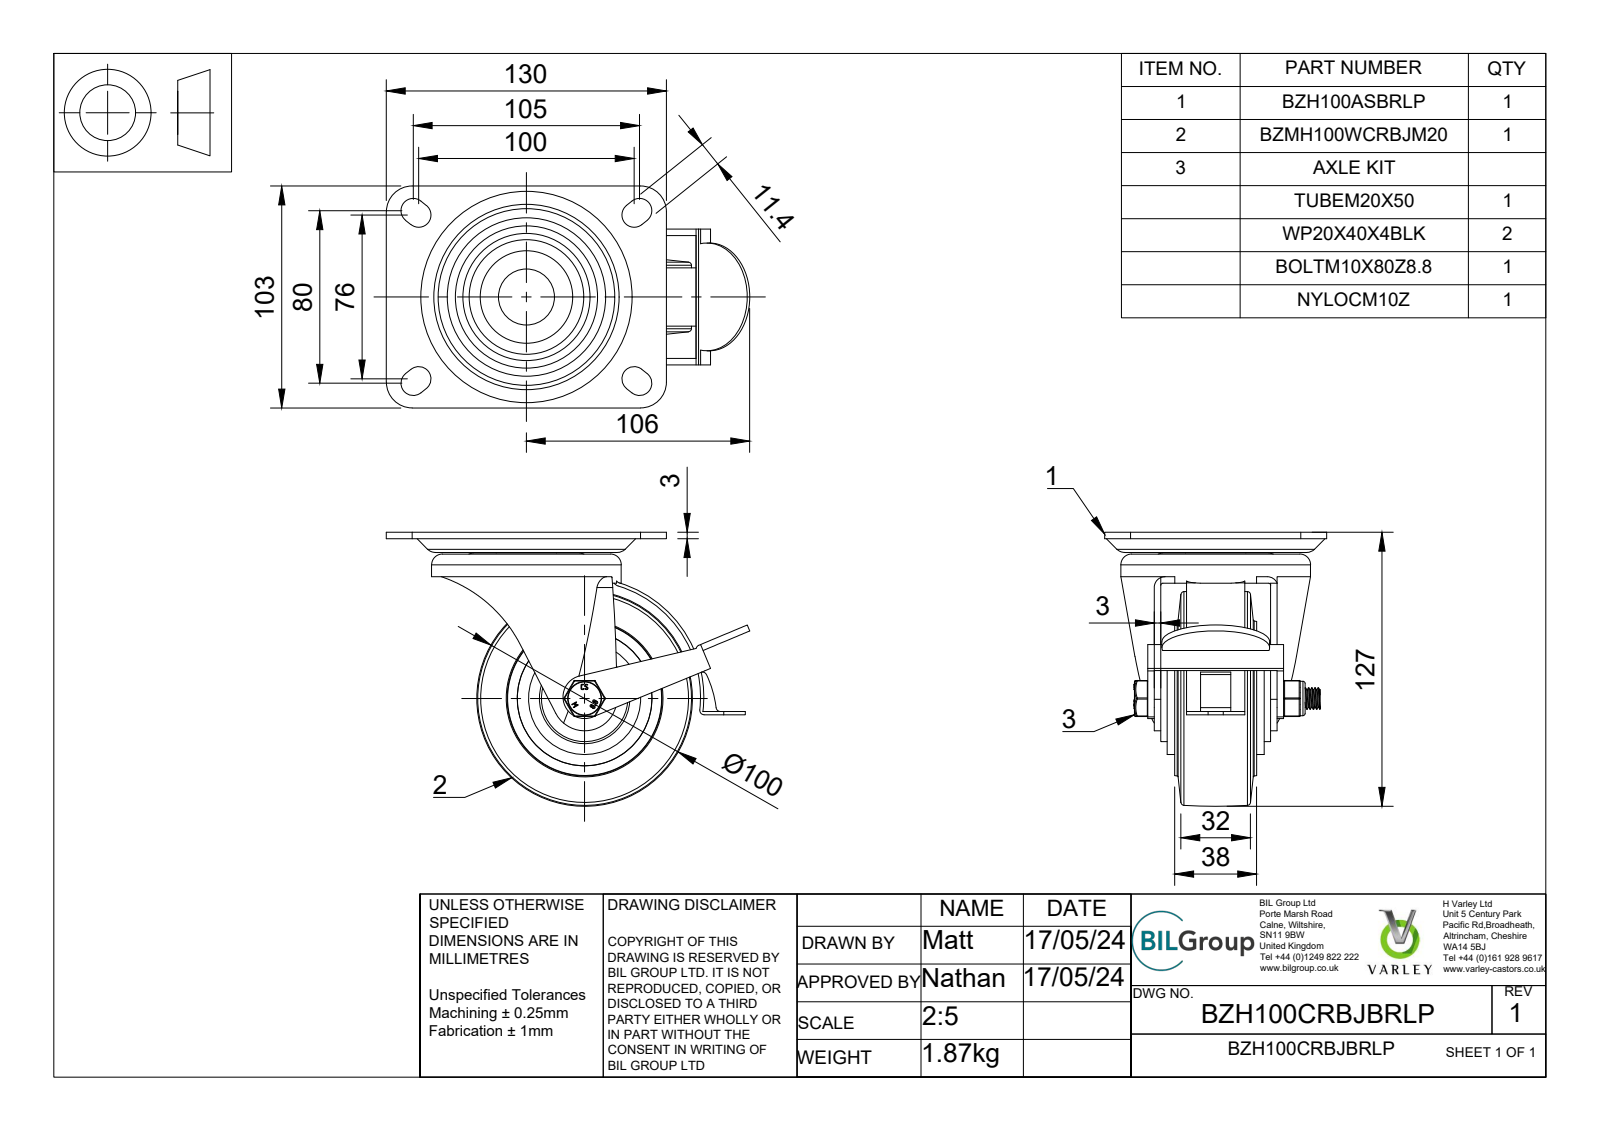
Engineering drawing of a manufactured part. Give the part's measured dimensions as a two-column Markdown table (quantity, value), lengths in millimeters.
| quantity | value |
| --- | --- |
| part name | BZH100CRBJBRLP v3; BZH100ASBRLP v1; ZINC PLATED, PRESSED STEEL TOP PLATE; ZINC PLATED, PRESSED STEEL FORKS (+8 more) |
| STEP written by | Autodesk Translation Framework v13.14.0.145 (AUTOMOTIVE_DESIGN) |
| units | millimeters |
| bodies | 41 solids, 1267 faces (474 planar, 256 cylindrical, 537 other) |
| overall size | 168.66 × 127.13 × 103 |
| volume | 390 404 mm³ |
| surface area | 165 145 mm² |
| round holes (diameter × count) | 10 × 1, 10.5 × 1, 12 × 1, 20 × 1, 21 × 1, 25 × 1, 26 × 1, 30 × 1, 35 × 1, 36 × 1, 38 × 1, 42 × 1 |
| round bosses / shafts (diameter × count) | 8 × 18, 88 × 1, 52 × 1, 40 × 1, 37 × 1, 36 × 1, 28 × 1, 27 × 1 |
| partial cylindrical surfaces (radius × count) | 0.5 × 18, 2 × 8, 5.7 × 8, 0.33 × 4, 0.64 × 4, 12 × 4, 10 × 3, 0.63 × 2 |
| main face-to-face distances | 3, 54, 6, 57, 51, 6.5, 44.5, 3.5, 9.5, 47.5 |
